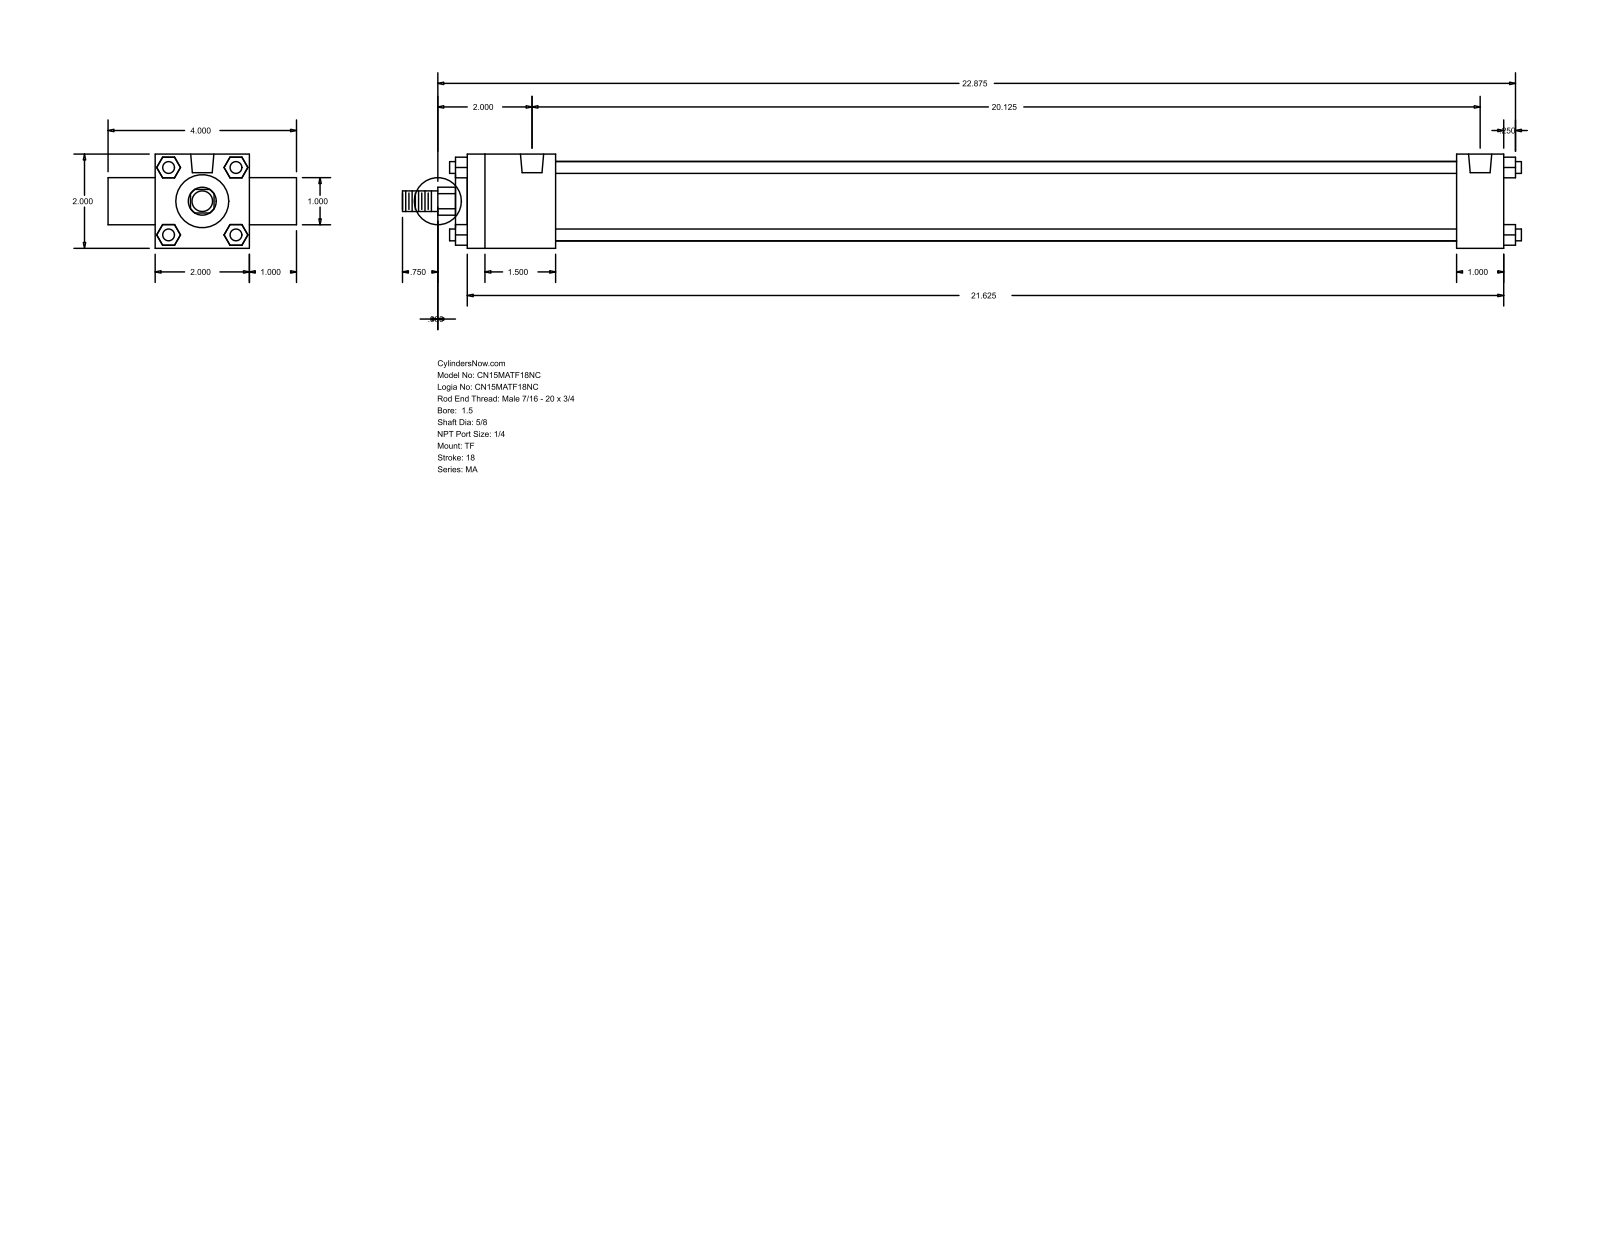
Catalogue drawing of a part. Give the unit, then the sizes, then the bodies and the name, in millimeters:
Units: millimetres
Overall size (bounding box): 603.25 × 101.6 × 50.8
Round holes (diameter × count): ⌀7.94 ×3, ⌀12.49 ×2
Round bosses / shafts (diameter × count): ⌀6.35 ×4, ⌀42.93 ×1, ⌀28.57 ×1, ⌀25.4 ×1, ⌀15.88 ×1, ⌀11.11 ×1
Partial cylindrical surfaces — rounded edges, fillets, slot ends (radius × count): R7.54 ×1
Main face-to-face distances: 50.8, 25.4, 558.79, 6.35, 565.14, 76.2, 47.62, 533.39, 485.77, 511.17
Hole centre spacings: 511.18
Bodies: 0 solids, 120 faces (92 planar, 28 cylindrical, 0 other)
Part name (STEP PRODUCT): MA_TF__0150_0.625
STEP written by: GSSL Pune (CONFIG_CONTROL_DESIGN)
